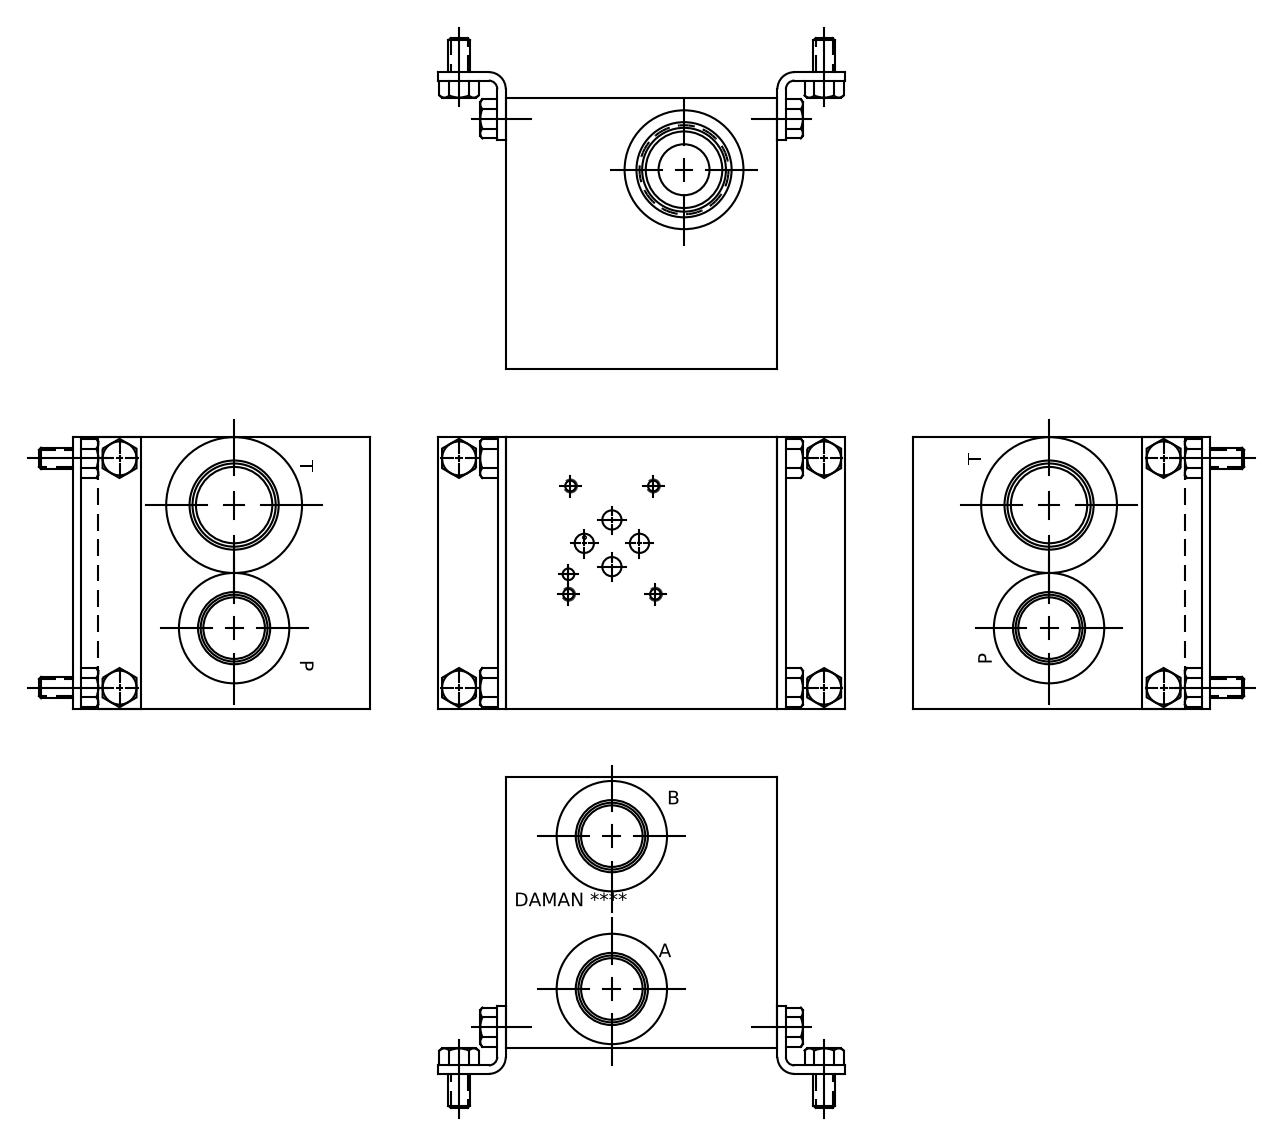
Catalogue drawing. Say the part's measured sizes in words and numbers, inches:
The part is named "Part_AD03HP012S_C_3D". Its 3-D file was written by "Autodesk Inventor 2020 (AUTOMOTIVE_DESIGN)". It is 1 solid with 563 faces: 323 planar, 57 cylindrical and 183 other. Overall it measures 4 by 4 by 4 inches. Its volume is 52.95 cubic inches and its surface area 133.8 square inches. Round holes: 4 of diameter 0.166, 4 of diameter 0.197, 3 of diameter 0.25, 3 of diameter 0.906, 3 of diameter 0.981, 3 of diameter 1.063, 3 of diameter 1.08, 3 of diameter 1.655, 2 of diameter 0.266, 2 of diameter 0.315, 2 of diameter 1.313, 1 of diameter 0.156. The main face-to-face distances are 4, 0.031, 3.969, 3.938, 3.849, 3.818, 0.151, 0.781, 0.75, 3.219. The hole center spacings are 0.868, 1.594, 2.026, 0.295, 0.512, 0.532, 0.532, 0.533.
